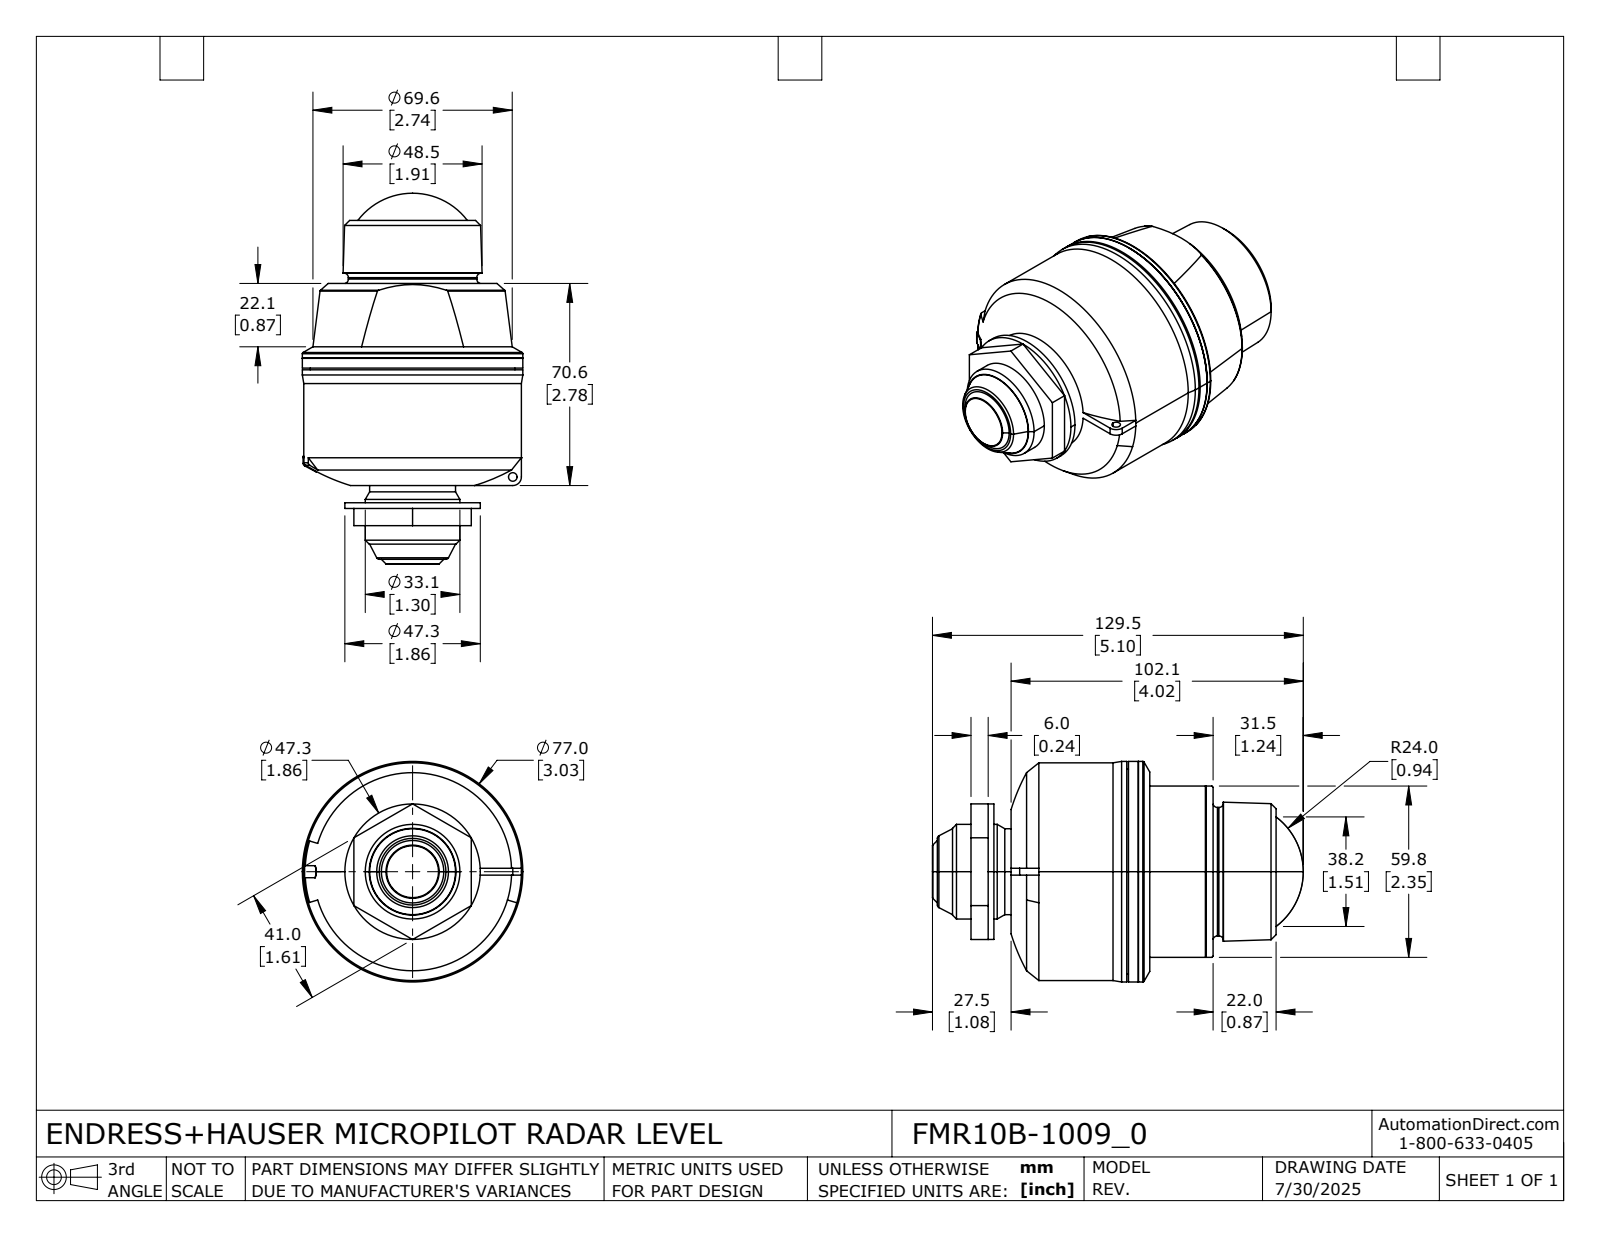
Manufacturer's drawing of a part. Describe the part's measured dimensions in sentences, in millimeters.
The part is named "FMR10B-1009_0". Its 3-D file was written by "SolidWorks 2024 (AUTOMOTIVE_DESIGN)". It is 1 solid with 125 faces: 43 planar, 31 cylindrical and 51 other. Overall it measures 129.5 by 77 by 77 millimeters. Its volume is 352 500 cubic millimeters and its surface area 32 520 square millimeters. Round holes: 1 of diameter 3. Round bosses or shafts: 1 of diameter 77, 1 of diameter 76, 1 of diameter 71.5, 1 of diameter 48.5, 1 of diameter 47.3, 1 of diameter 44.9, 1 of diameter 33, 1 of diameter 30. Partial cylindrical surfaces (rounded edges, fillets, slot ends): 2 of radius 5, 1 of radius 1, 1 of radius 3. The main face-to-face distances are 6, 41, 8, 76.6, 70.6, 29.5, 30.1, 0.6, 47, 40.4.
